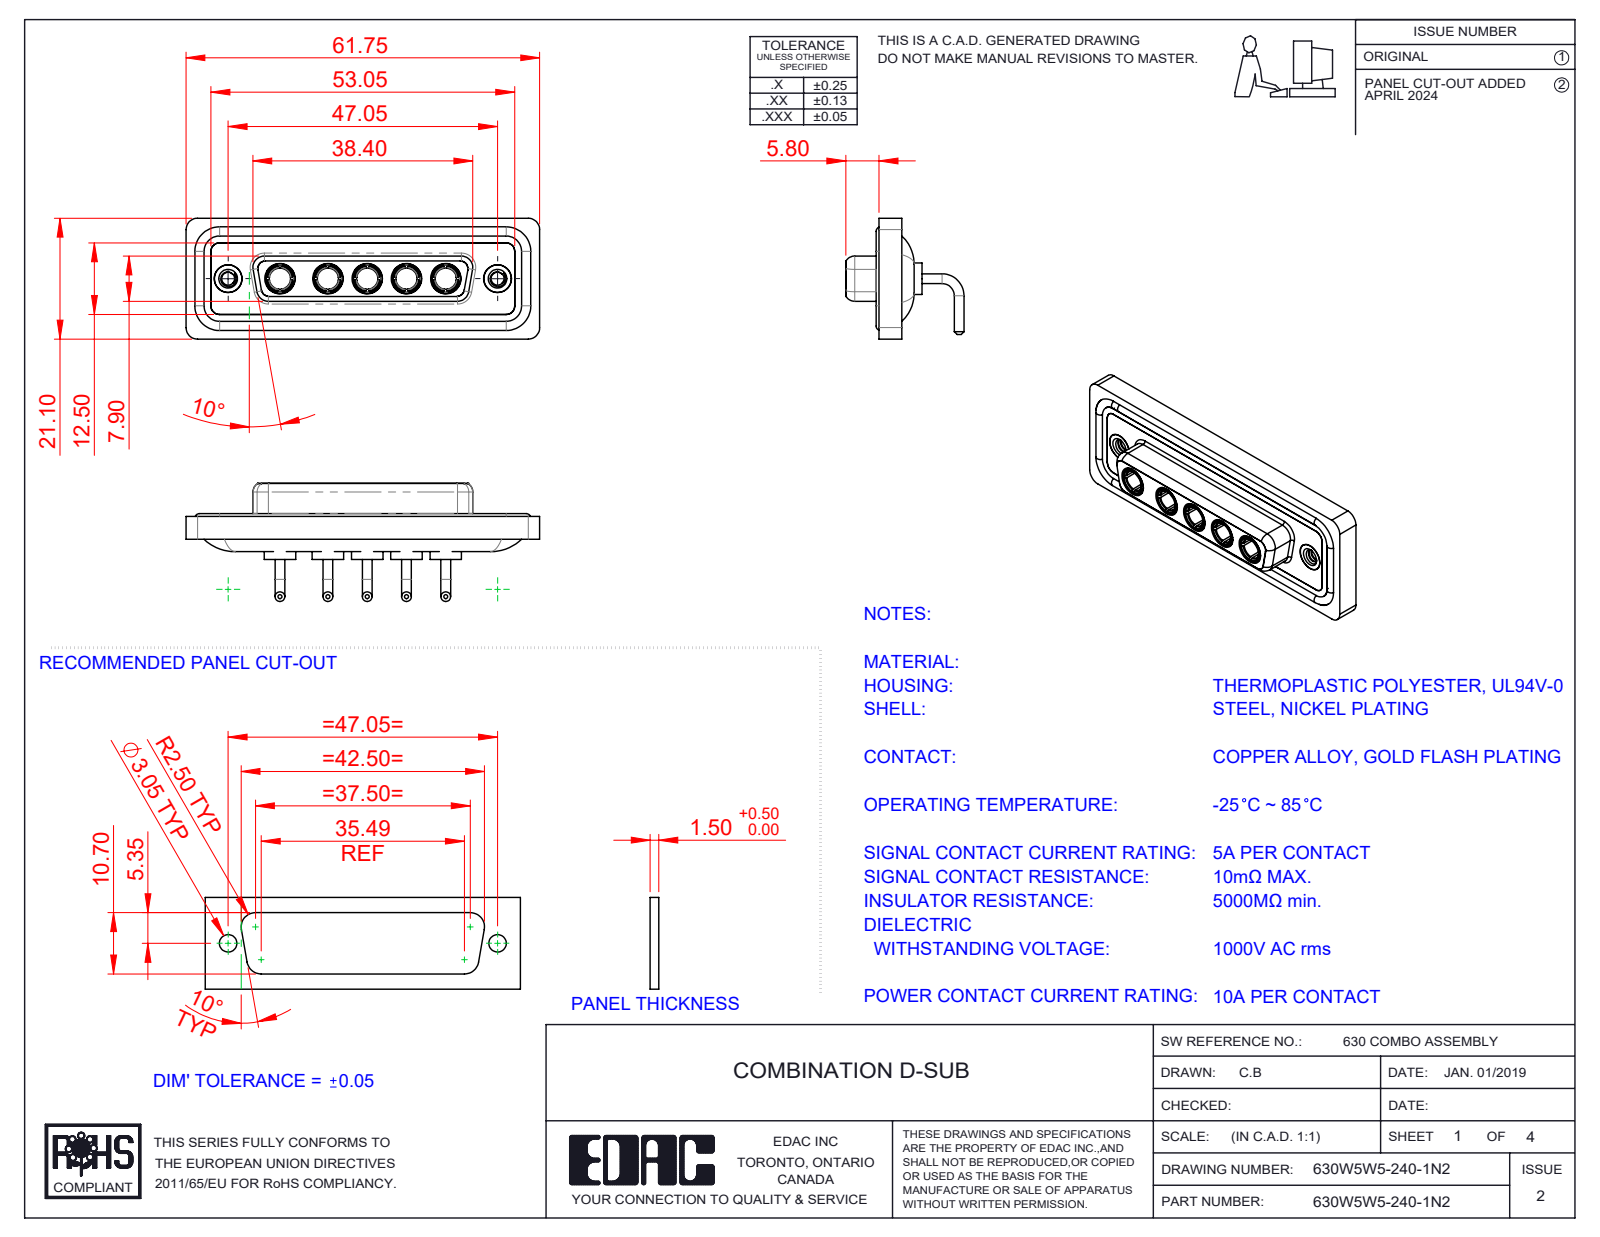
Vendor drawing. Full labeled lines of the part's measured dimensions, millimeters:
Part name (STEP PRODUCT): 630Combo Housing_5W5; 630Combo Waterproof Housing_25 Contacts; 630Combo Shell Front_25 Contacts; 630Combo Threaded Rivet_2 (+3 more)
STEP written by: SolidWorks 2023 (CONFIG_CONTROL_DESIGN)
Units: millimetres
Bodies: 17 solids, 776 faces (250 planar, 313 cylindrical, 213 other)
Overall size (bounding box): 61.75 × 21.1 × 20.65
Volume: 8 146 mm³ · Surface area: 13 559 mm²
Round holes (diameter × count): ⌀4.85 ×7, ⌀3.7 ×5, ⌀5.3 ×5, ⌀2.26 ×2, ⌀4 ×2, ⌀4.05 ×2, ⌀5 ×2
Round bosses / shafts (diameter × count): ⌀1.7 ×10, ⌀5.5 ×5, ⌀5.2 ×5, ⌀4.96 ×5, ⌀4.75 ×5, ⌀3.75 ×5, ⌀1.6 ×4, ⌀4.95 ×2
Partial cylindrical surfaces — rounded edges, fillets, slot ends (radius × count): R1.5 ×18, R2 ×18, R1.35 ×8, R1.6 ×8, R2.1 ×5, R0.25 ×4, R0.5 ×4, R0.6 ×4
Main face-to-face distances: 0.4, 1.8, 4.1, 1.1, 1.5, 2.5, 3.1, 3.7, 1.6, 1.35
Hole centre spacings: 6.86, 9.04, 38.01, 6.87, 8.38, 13.72, 13.73, 15.25
